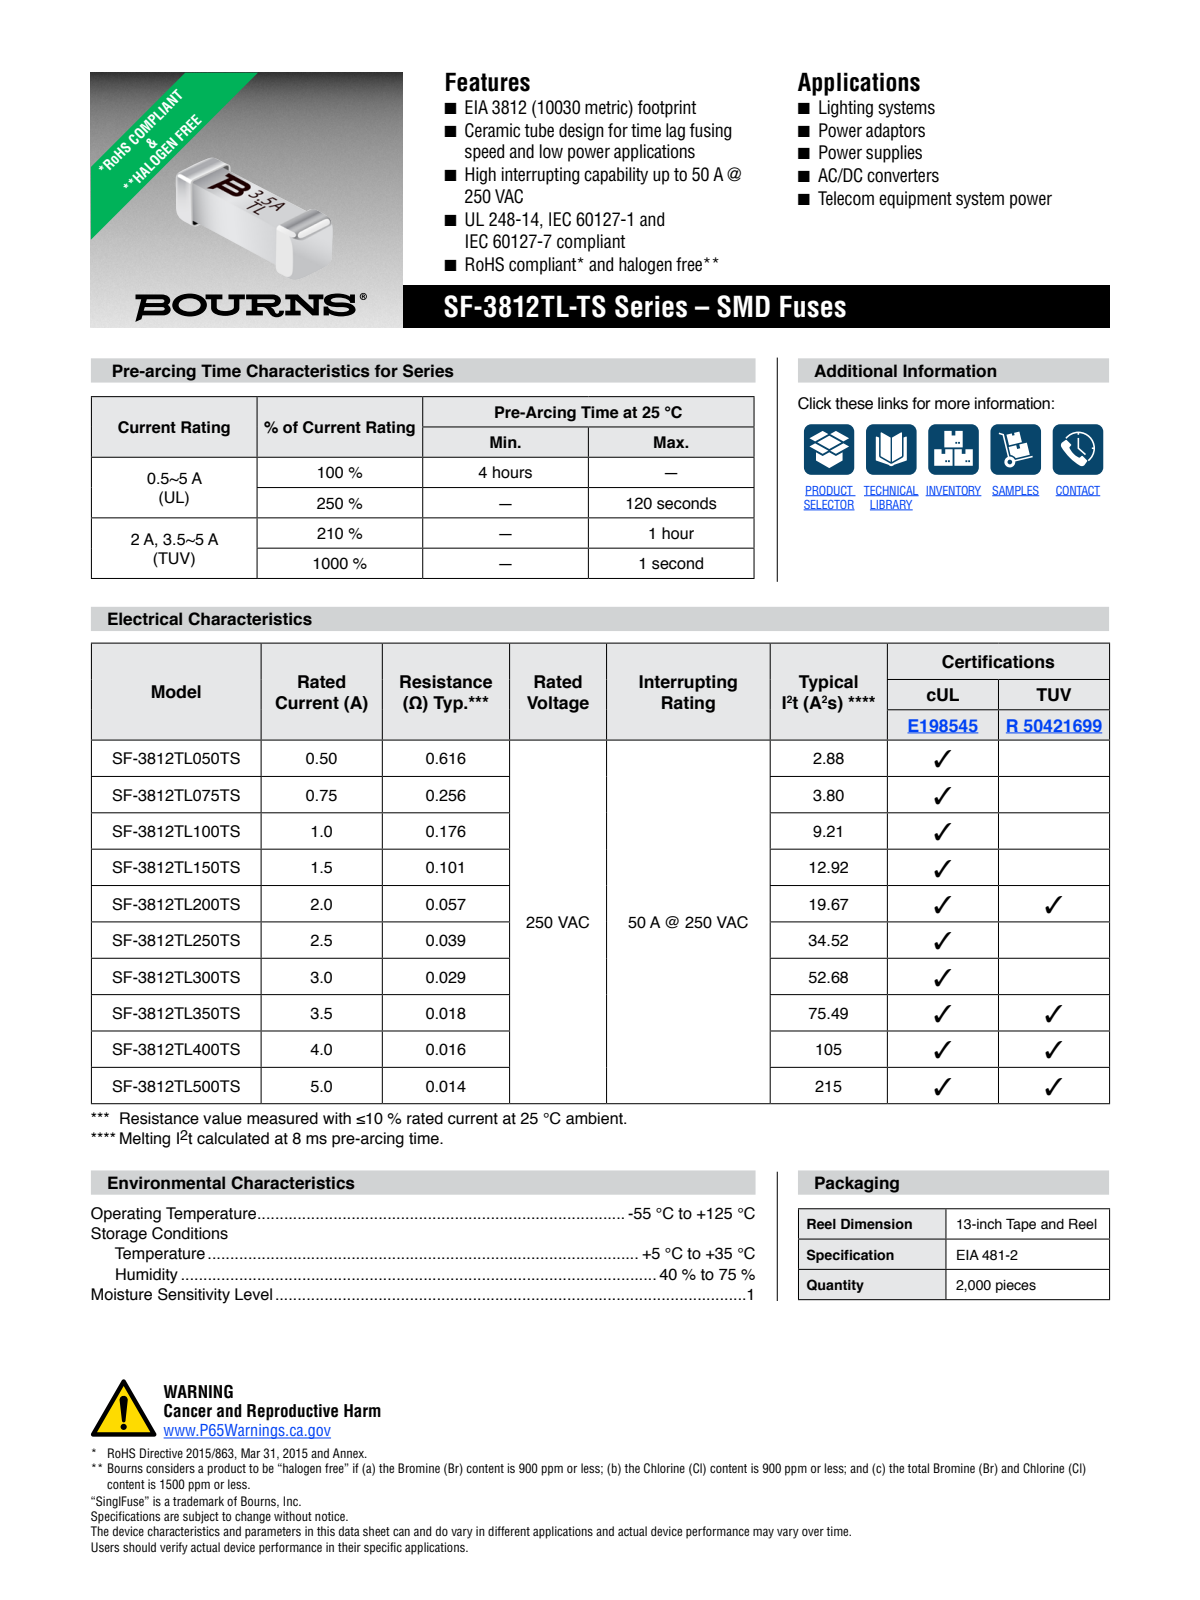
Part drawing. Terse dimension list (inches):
name: sF-3812TL-TS
written by: SolidWorks 2021 (AUTOMOTIVE_DESIGN)
unit: in
bodies: 1 solid, 40 faces (16 planar, 16 cylindrical, 8 other)
size: 0.398 × 0.122 × 0.122
volume: 0.005 in³; area: 0.207 in²
rounds: 12× R0.01
face distances: 0.104, 0.113, 0.122, 0.398, 0.069, 0.329, 0.329, 0.26, 0.069
